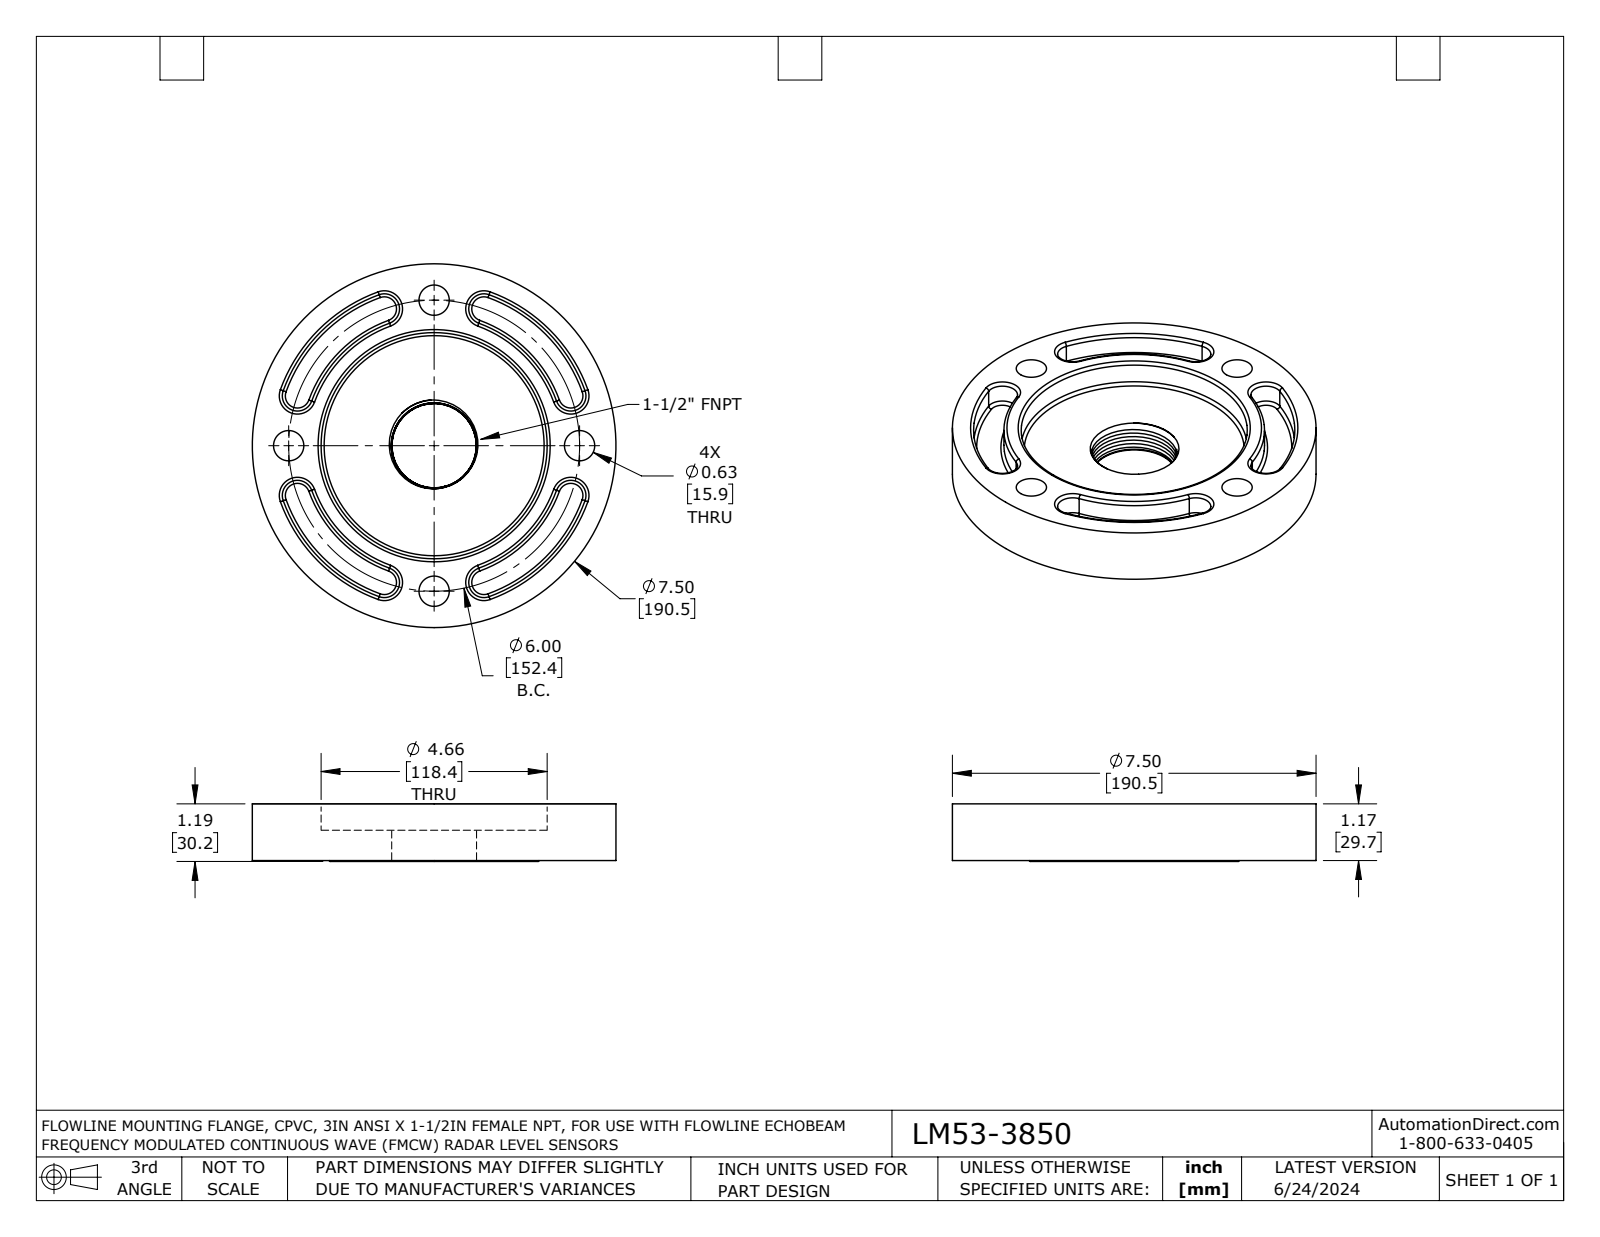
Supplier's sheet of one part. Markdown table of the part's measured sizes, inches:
| quantity | value |
| --- | --- |
| part name | LM53-3850 |
| STEP written by | SolidWorks 2021 (AUTOMOTIVE_DESIGN) |
| units | inches |
| bodies | 1 solid, 161 faces (18 planar, 34 cylindrical, 109 other) |
| overall size | 7.5 × 7.5 × 1.188 |
| volume | 35.5 in³ |
| surface area | 146.5 in² |
| round holes (diameter × count) | 0.625 × 4, 1.736 × 1, 4.662 × 1 |
| round bosses / shafts (diameter × count) | 7.5 × 1 |
| partial cylindrical surfaces (radius × count) | 0.313 × 8, 2.688 × 1, 3.313 × 1 |
| main face-to-face distances | 1.169, 0.625, 0.544, 0.669, 0.044, 0.5 |
| hole center spacings | 3, 4.243, 6 |
